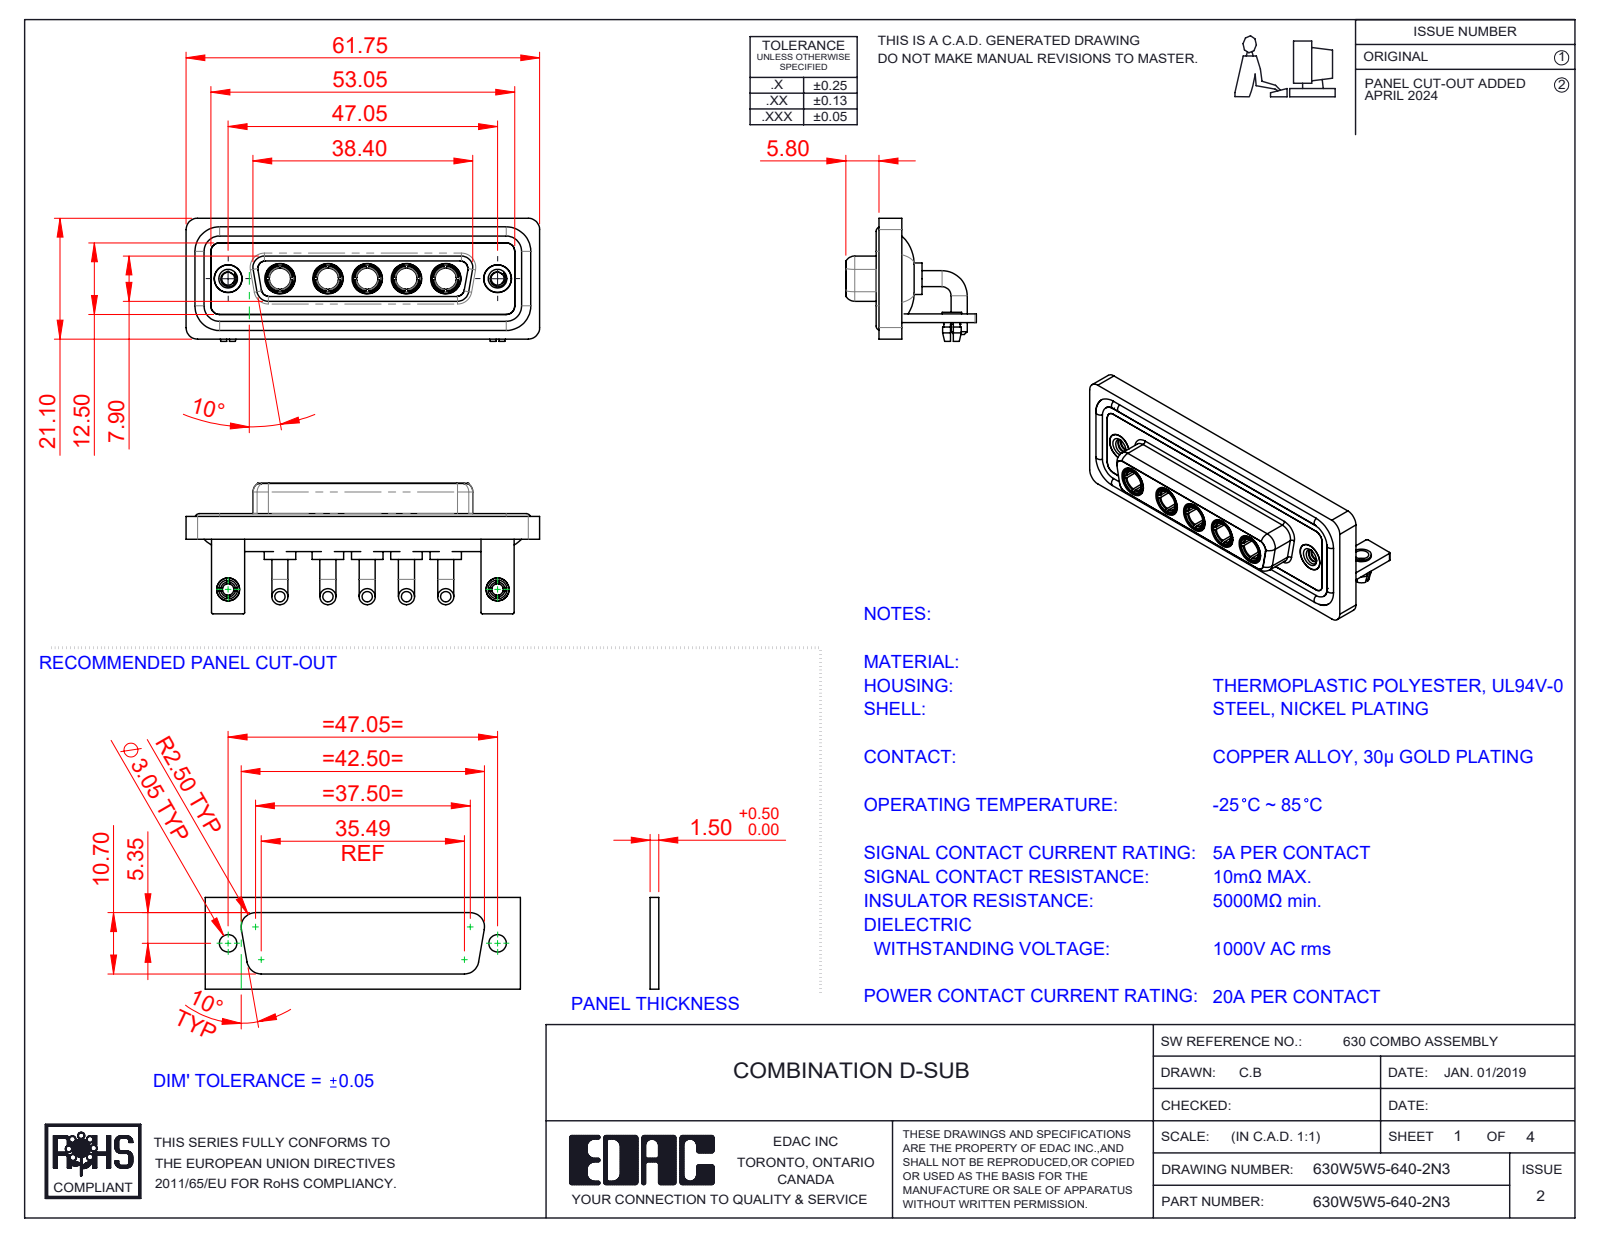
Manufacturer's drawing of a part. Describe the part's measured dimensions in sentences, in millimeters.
The part is named "630Combo Shell Rear_25 Contacts; 630Combo Housing_5W5; 630Combo Stabilizer Bracket_50 Contacts; Power Socket_20A RA (+5 more)". Its 3-D file was written by "SolidWorks 2023 (CONFIG_CONTROL_DESIGN)". It is 21 solids with 916 faces: 318 planar, 369 cylindrical and 229 other. Overall it measures 61.75 by 22.8 by 21.5 millimeters. Its volume is 8 838 cubic millimeters and its surface area 14 759 square millimeters. Round holes: 7 of diameter 4.85, 5 of diameter 3.7, 5 of diameter 5.3, 2 of diameter 2, 2 of diameter 2.26, 2 of diameter 2.5, 2 of diameter 3.2, 2 of diameter 4, 2 of diameter 4.05, 2 of diameter 5. Round bosses or shafts: 10 of diameter 2.8, 5 of diameter 5.5, 5 of diameter 5.2, 5 of diameter 4.96, 5 of diameter 4.75, 5 of diameter 3.75, 4 of diameter 1.6, 2 of diameter 4.95. Partial cylindrical surfaces (rounded edges, fillets, slot ends): 19 of radius 2, 18 of radius 1.5, 16 of radius 0.25, 8 of radius 1.35, 8 of radius 1.6, 5 of radius 0.5, 5 of radius 2.1, 4 of radius 0.6. The main face-to-face distances are 0.4, 1.8, 2.9, 1.5, 3.7, 4.1, 1.1, 1.4, 1.6, 2.5. The hole center spacings are 6.86, 9.04, 38.01, 47.05, 6.87, 8.38, 13.72, 13.73.
